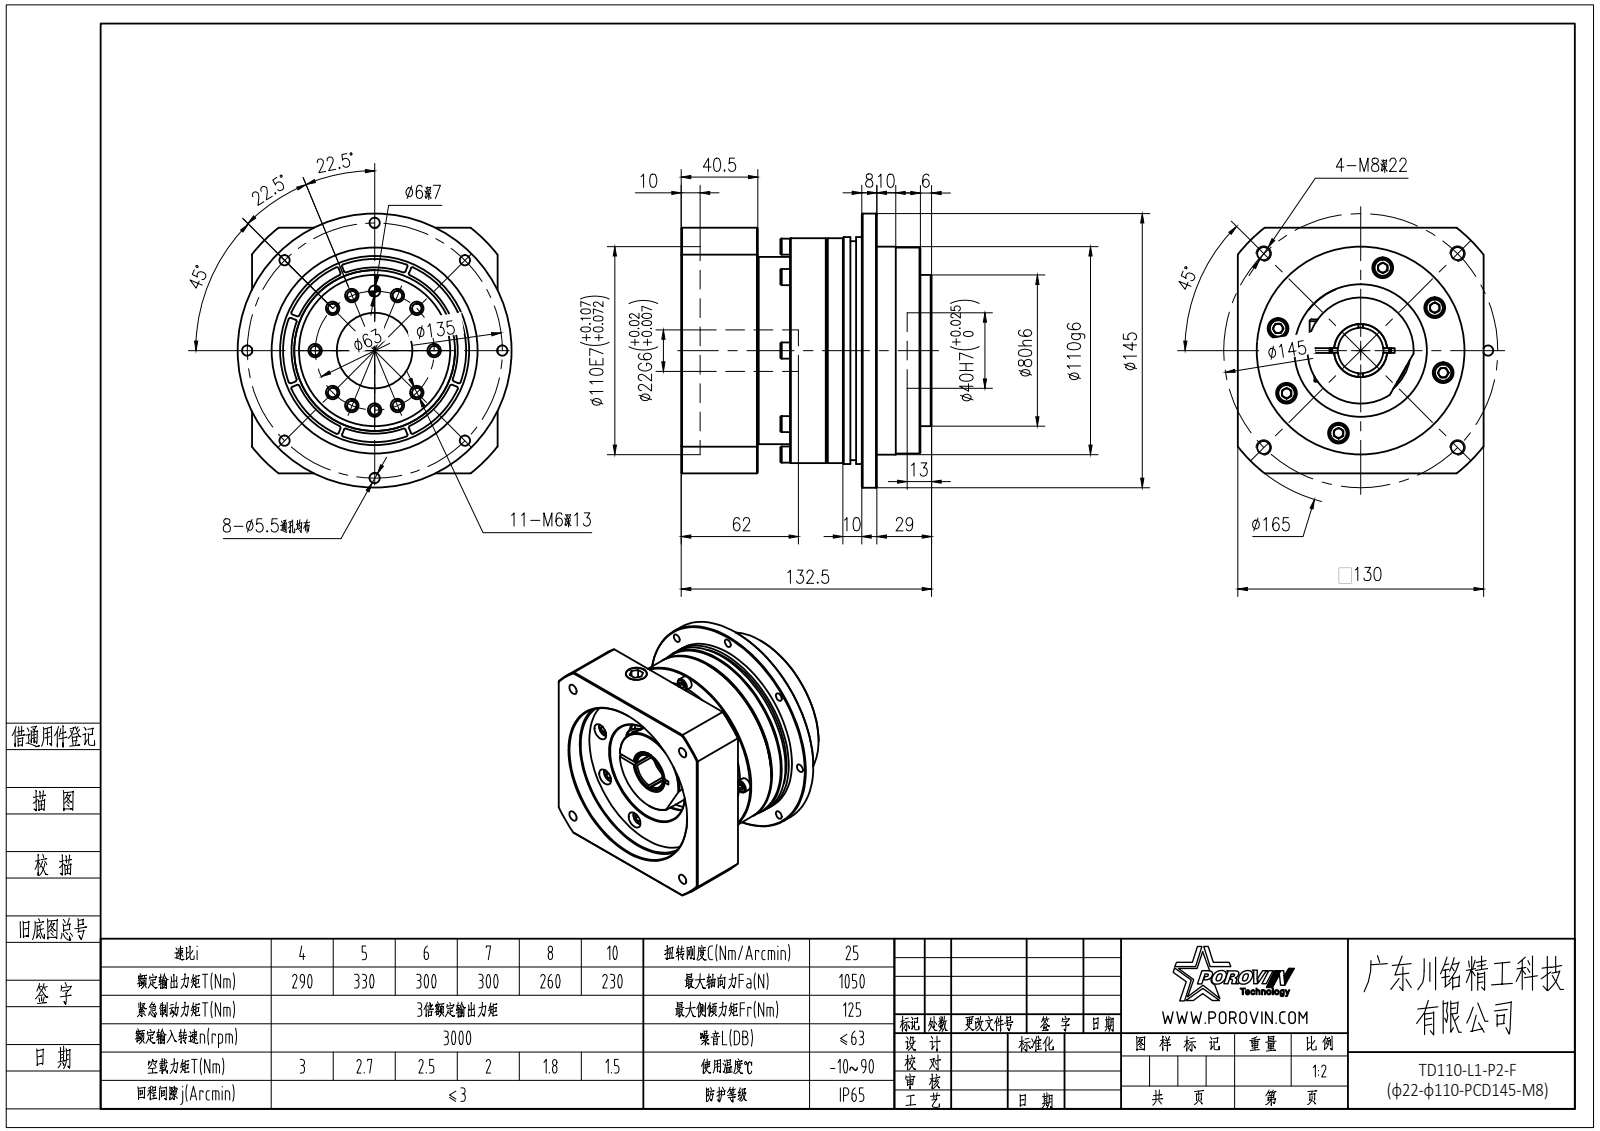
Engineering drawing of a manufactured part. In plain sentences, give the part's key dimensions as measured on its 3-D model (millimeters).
The part is named "hexagon socket head cap screws gb_GB_FASTENER_SCREWS_HSHCS M6X20-N; hexagon socket head cap screws gb_GB_FASTENER_SCREWS_HSHCS M8X25-N; 一级齿圈外形图加法兰盘 KD110; KD110L1-110-22-60-M8-145 (+4 more)". Its 3-D file was written by "SolidWorks 2016 (CONFIG_CONTROL_DESIGN)". It is 37 solids with 1041 faces: 416 planar, 405 cylindrical and 220 other. Overall it measures 145 by 145 by 132.5 millimeters. Its volume is 1 226 000 cubic millimeters and its surface area 208 515 square millimeters. Round holes: 17 of diameter 5, 16 of diameter 5.5, 11 of diameter 7, 8 of diameter 5.4, 6 of diameter 6.6, 6 of diameter 6.68, 6 of diameter 11, 5 of diameter 6.8, 1 of diameter 6, 1 of diameter 9, 1 of diameter 14, 1 of diameter 22. Round bosses or shafts: 9 of diameter 8, 8 of diameter 8.5, 8 of diameter 5, 6 of diameter 10, 6 of diameter 9.88, 6 of diameter 6, 1 of diameter 145, 1 of diameter 120. Partial cylindrical surfaces (rounded edges, fillets, slot ends): 32 of radius 1, 1 of radius 82.5. The main face-to-face distances are 36.5, 103.5, 18, 18.5, 38, 130, 26.5, 55, 63, 40.5. The hole center spacings are 39.59, 48.28, 63.38, 74.49, 80.42, 87.07, 113.28, 58.2.
